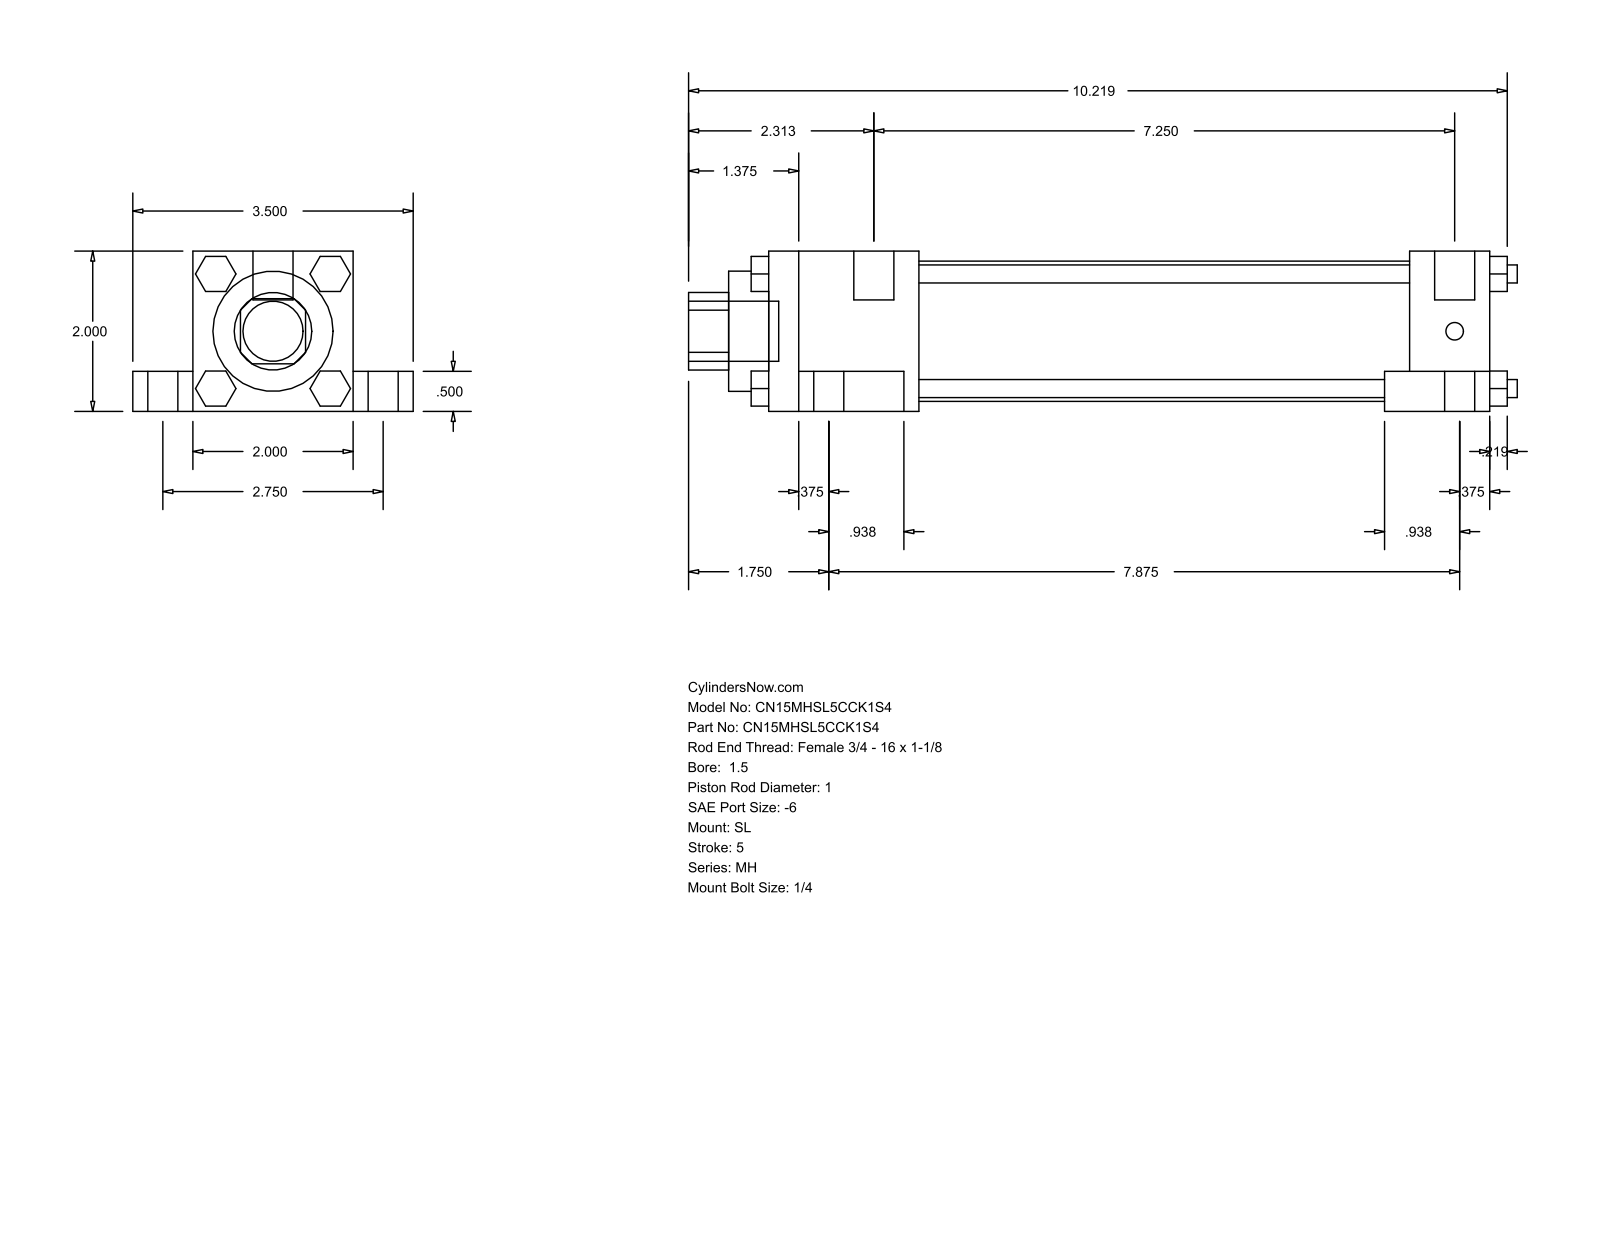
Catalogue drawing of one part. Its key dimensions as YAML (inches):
part_name: "MH_SL__0150_1"
step_written_by: "GSSL Pune (CONFIG_CONTROL_DESIGN)"
units: inches
bodies: {solids: 0, faces: 148, planar: 112, cylindrical: 36, other: 0}
overall_size: [10.344, 3.5, 2]
round_holes:
  - {diameter: 1, count: 1}
  - {diameter: 1.5, count: 1}
  - {diameter: 1.75, count: 1}
round_bosses_or_shafts:
  - {diameter: 0.625, count: 4}
  - {diameter: 0.375, count: 4}
  - {diameter: 0.225, count: 4}
  - {diameter: 0.219, count: 4}
  - {diameter: 0.5, count: 2}
  - {diameter: 0.75, count: 1}
partial_cylinders:
  - {radius: 0.484, count: 1}
face_to_face_distances: [2, 0.5, 1.5, 0.75, 2.75, 9, 1, 0.375, 1.313, 7.313]
